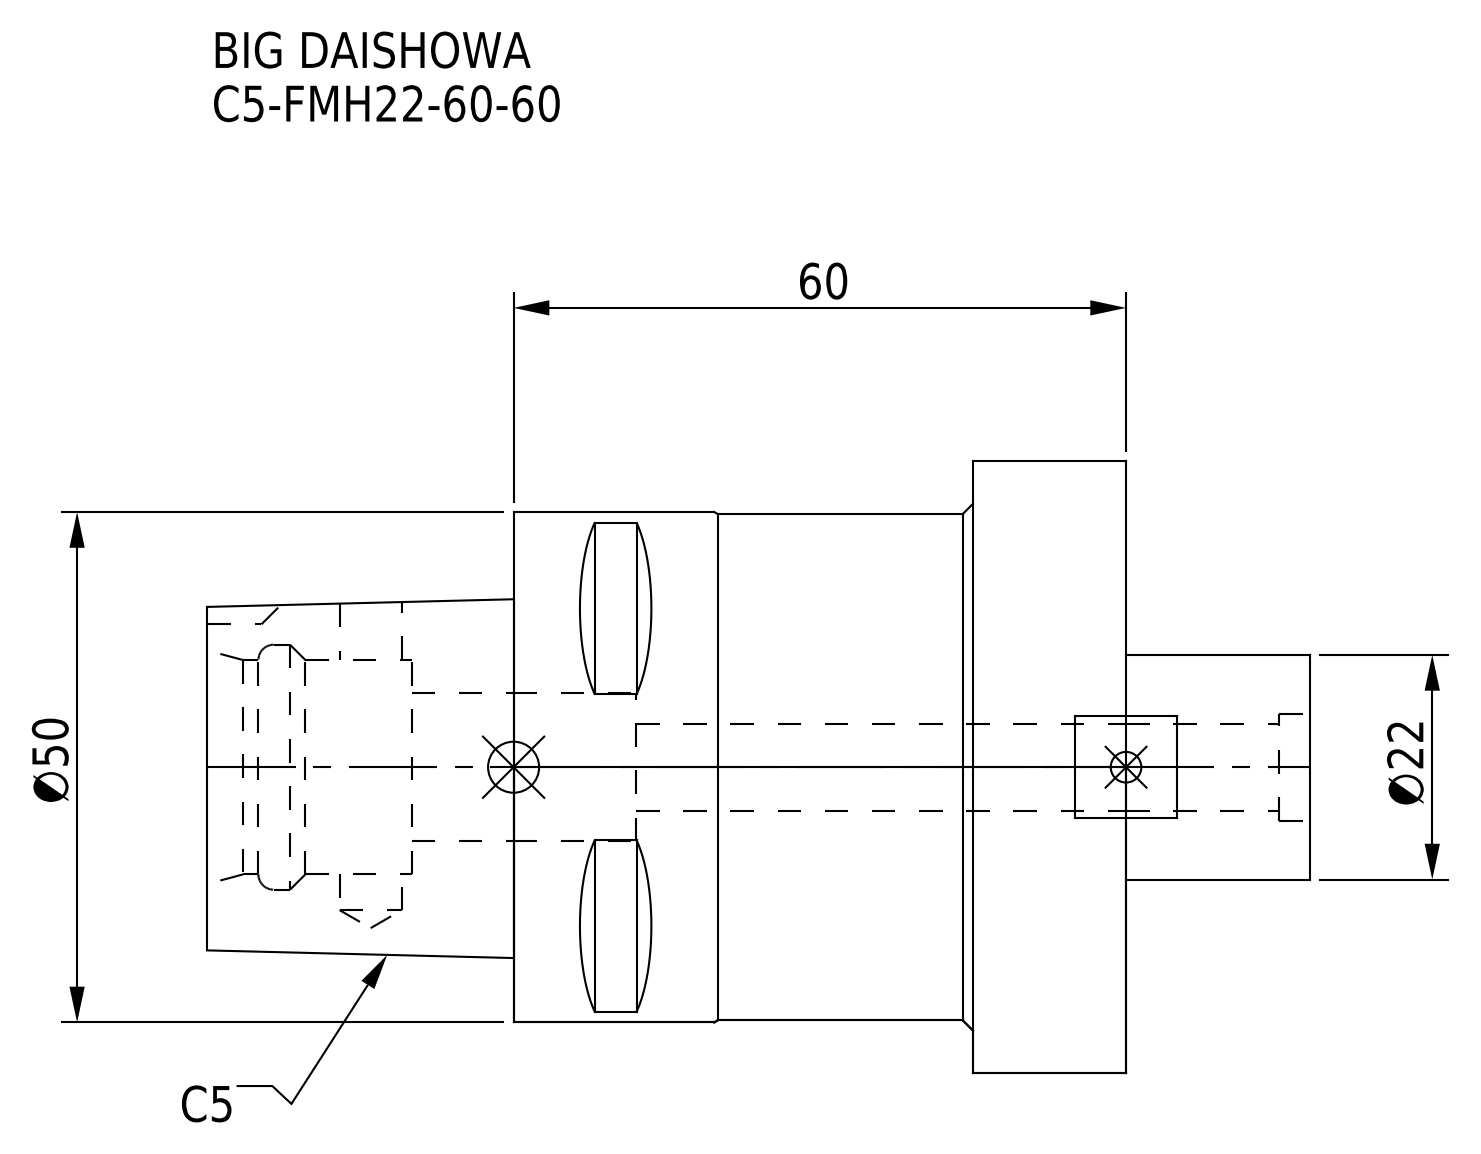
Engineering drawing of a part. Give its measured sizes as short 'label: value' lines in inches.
name: C5-FMH22-60-60
written by: CREO PARAMETRIC BY PTC INC, 2016380 (AUTOMOTIVE_DESIGN)
unit: in
bodies: 1 solid, 79 faces (40 planar, 25 cylindrical, 14 other)
size: 4.252 × 2.362 × 2.362
volume: 9.159 in³; area: 38.51 in²
holes: 1× ⌀0.24, 1× ⌀0.335, 1× ⌀0.413, 1× ⌀0.571, 1× ⌀0.827, 1× ⌀0.945
bosses: 1× ⌀2.362, 1× ⌀1.969, 1× ⌀1.953, 1× ⌀0.866
rounds: 1× R0.157
face distances: 2.362, 0.591, 1.772, 2.953, 0.787, 1.181, 1.299, 0.709, 0.394, 3.543
